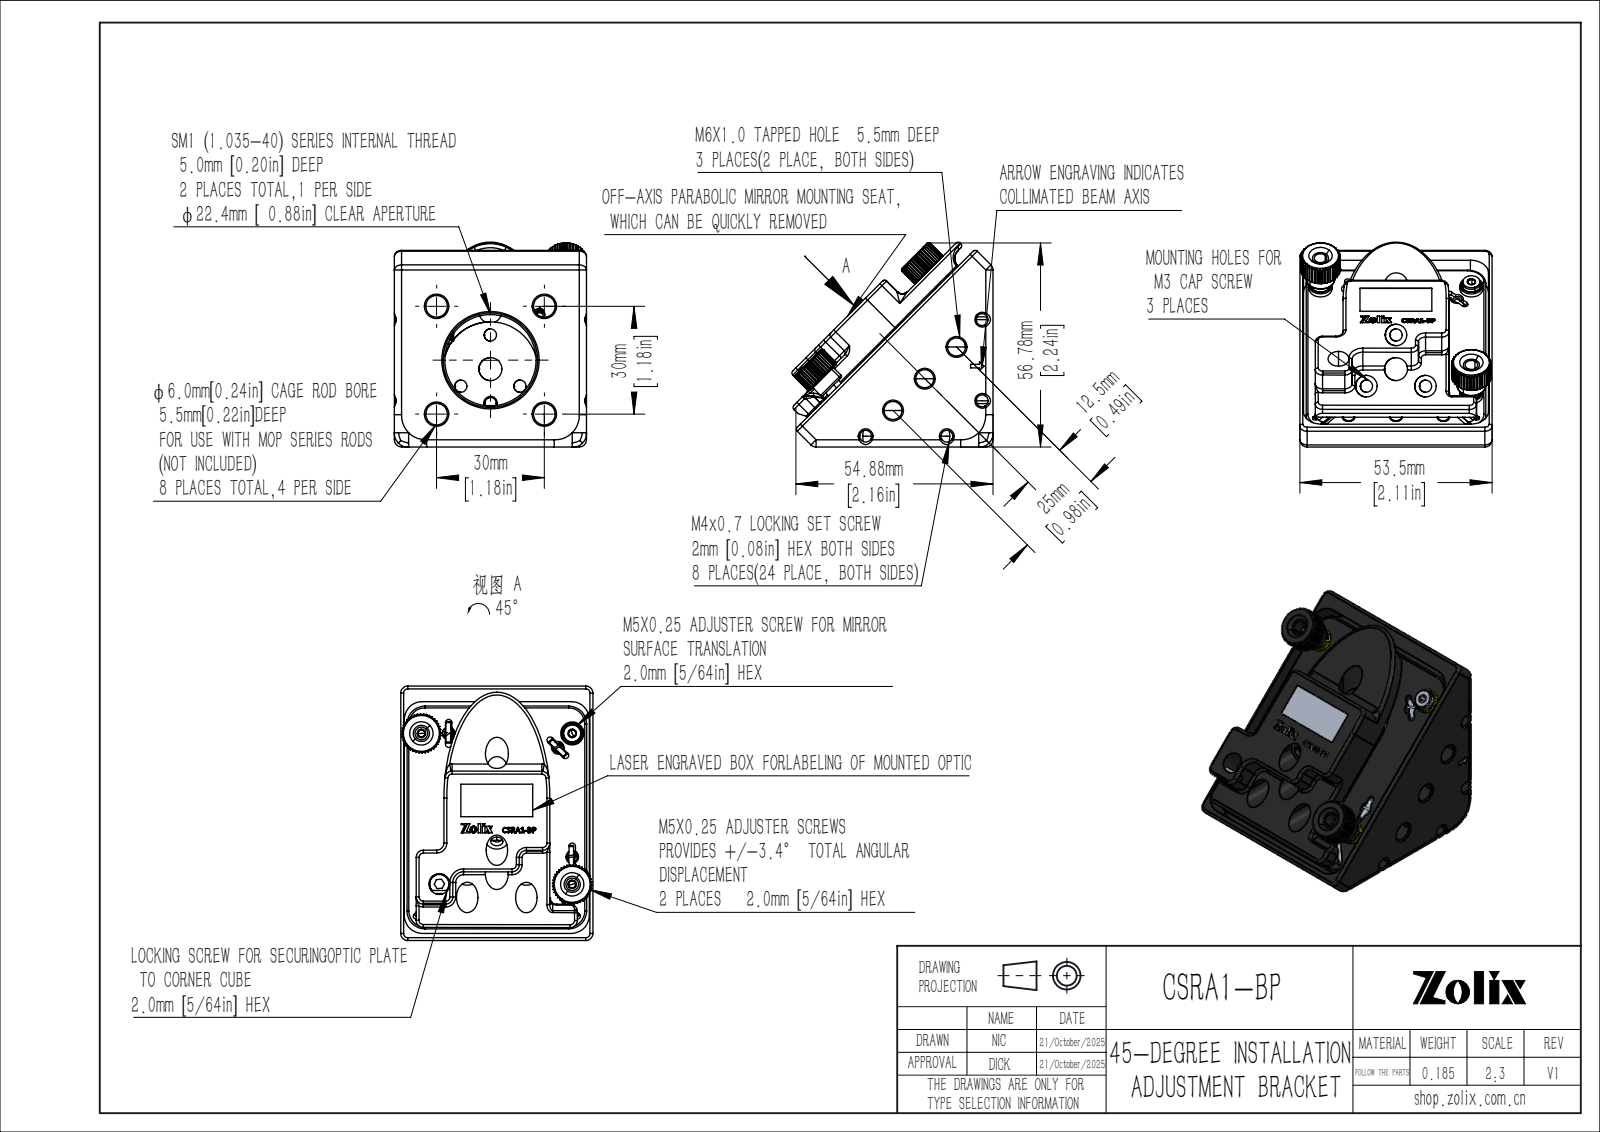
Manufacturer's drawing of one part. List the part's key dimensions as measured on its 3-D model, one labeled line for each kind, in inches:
Part name (STEP PRODUCT): CSRA1-BP
STEP written by: SolidWorks 2020 (CONFIG_CONTROL_DESIGN)
Units: inches
Bodies: 42 solids, 1579 faces (657 planar, 457 cylindrical, 465 other)
Overall size (bounding box): 2.244 × 2.205 × 2.106
Volume: 4.171 in³ · Surface area: 57 in²
Round holes (diameter × count): ⌀0.236 ×12, ⌀0.118 ×10, ⌀0.197 ×8, ⌀0.138 ×5, ⌀0.252 ×5, ⌀0.13 ×4, ⌀0.134 ×4, ⌀0.157 ×4, ⌀0.077 ×3, ⌀0.081 ×3, ⌀0.098 ×3, ⌀0.125 ×3
Round bosses / shafts (diameter × count): ⌀0.059 ×9, ⌀0.118 ×6, ⌀0.28 ×3, ⌀0.252 ×3, ⌀0.236 ×3, ⌀0.315 ×2, ⌀0.217 ×1, ⌀0.197 ×1
Partial cylindrical surfaces — rounded edges, fillets, slot ends (radius × count): R0.031 ×40, R0.079 ×26, R0.02 ×13, R0.03 ×12, R0.197 ×8, R0.035 ×6, R0.012 ×4, R0.118 ×4
Main face-to-face distances: 0.079, 0.28, 0.201, 0.039, 2.106, 0.358, 2.067, 0.118, 0.289, 0.161
Hole centre spacings: 0.835, 1.181, 1.654, 0.374, 1.504, 1.984, 2.183, 2.249
